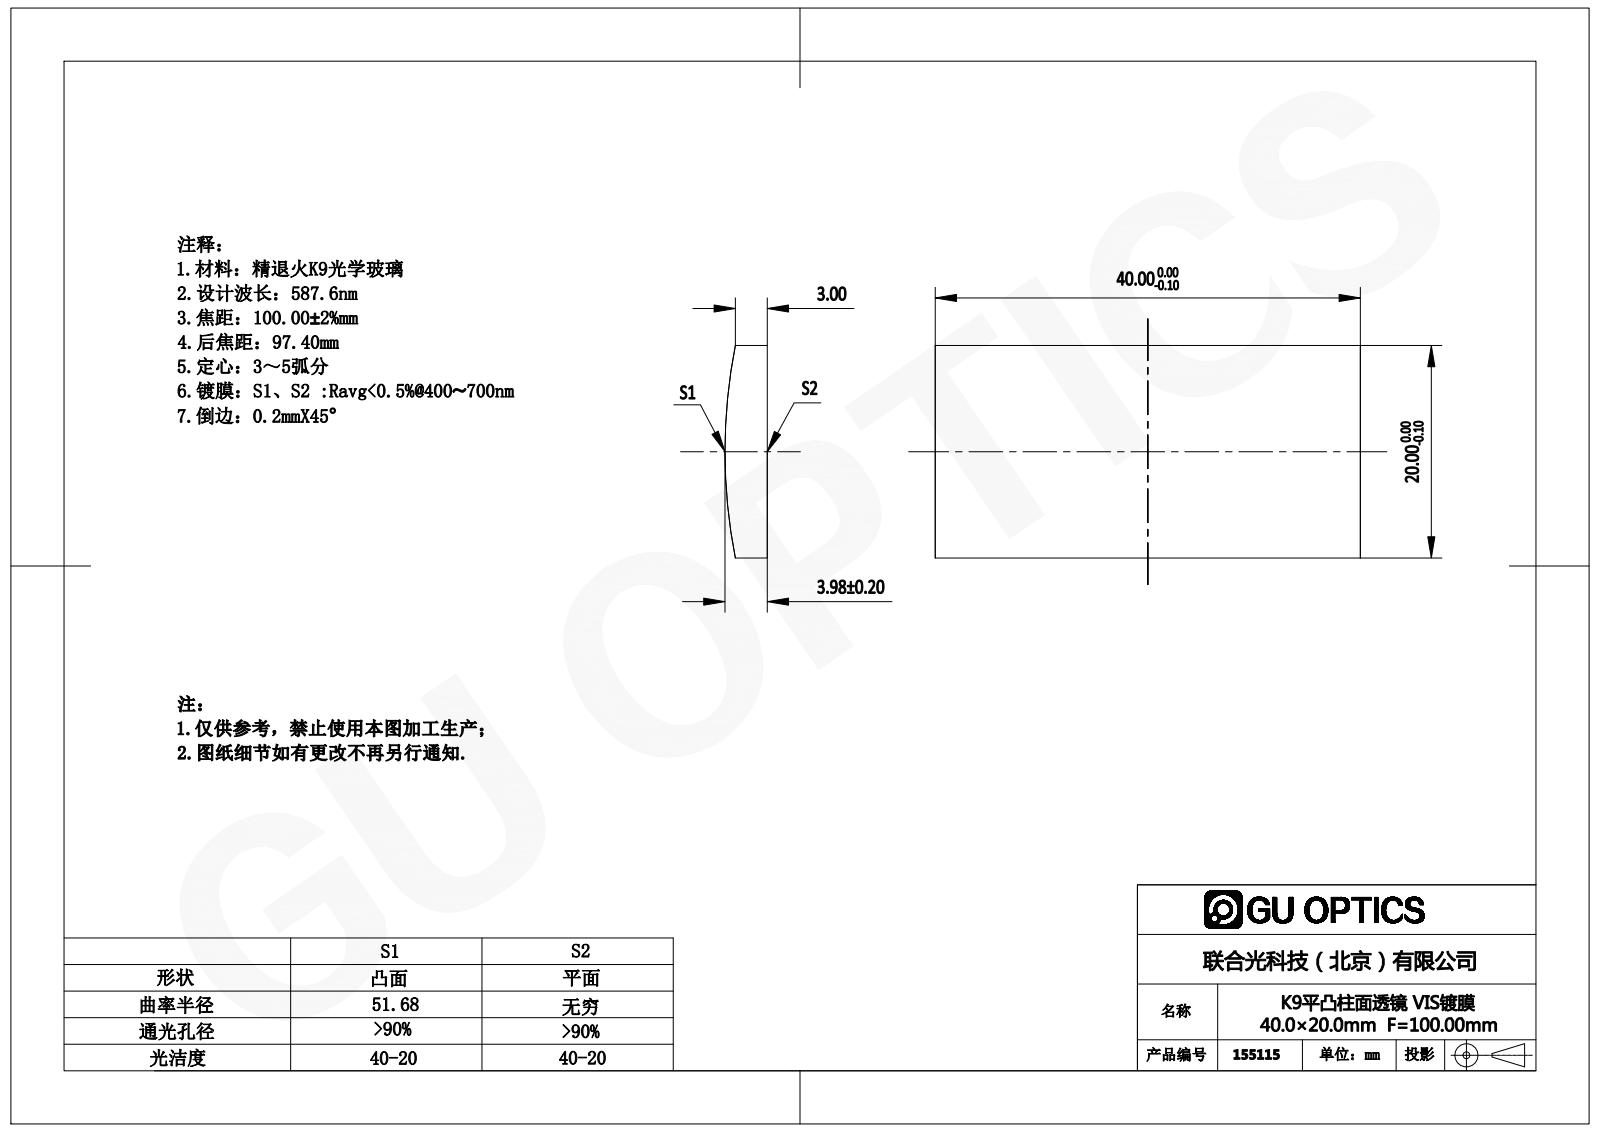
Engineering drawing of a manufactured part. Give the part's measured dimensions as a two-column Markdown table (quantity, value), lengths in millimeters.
| quantity | value |
| --- | --- |
| part name | 155049 |
| STEP written by | SolidWorks 2016 (AUTOMOTIVE_DESIGN) |
| units | millimeters |
| bodies | 1 solid, 6 faces (5 planar, 1 cylindrical, 0 other) |
| overall size | 40 × 20 × 3.98 |
| volume | 2 925 mm³ |
| surface area | 1 992 mm² |
| partial cylindrical surfaces (radius × count) | 51.68 × 1 |
| main face-to-face distances | 20, 40 |
